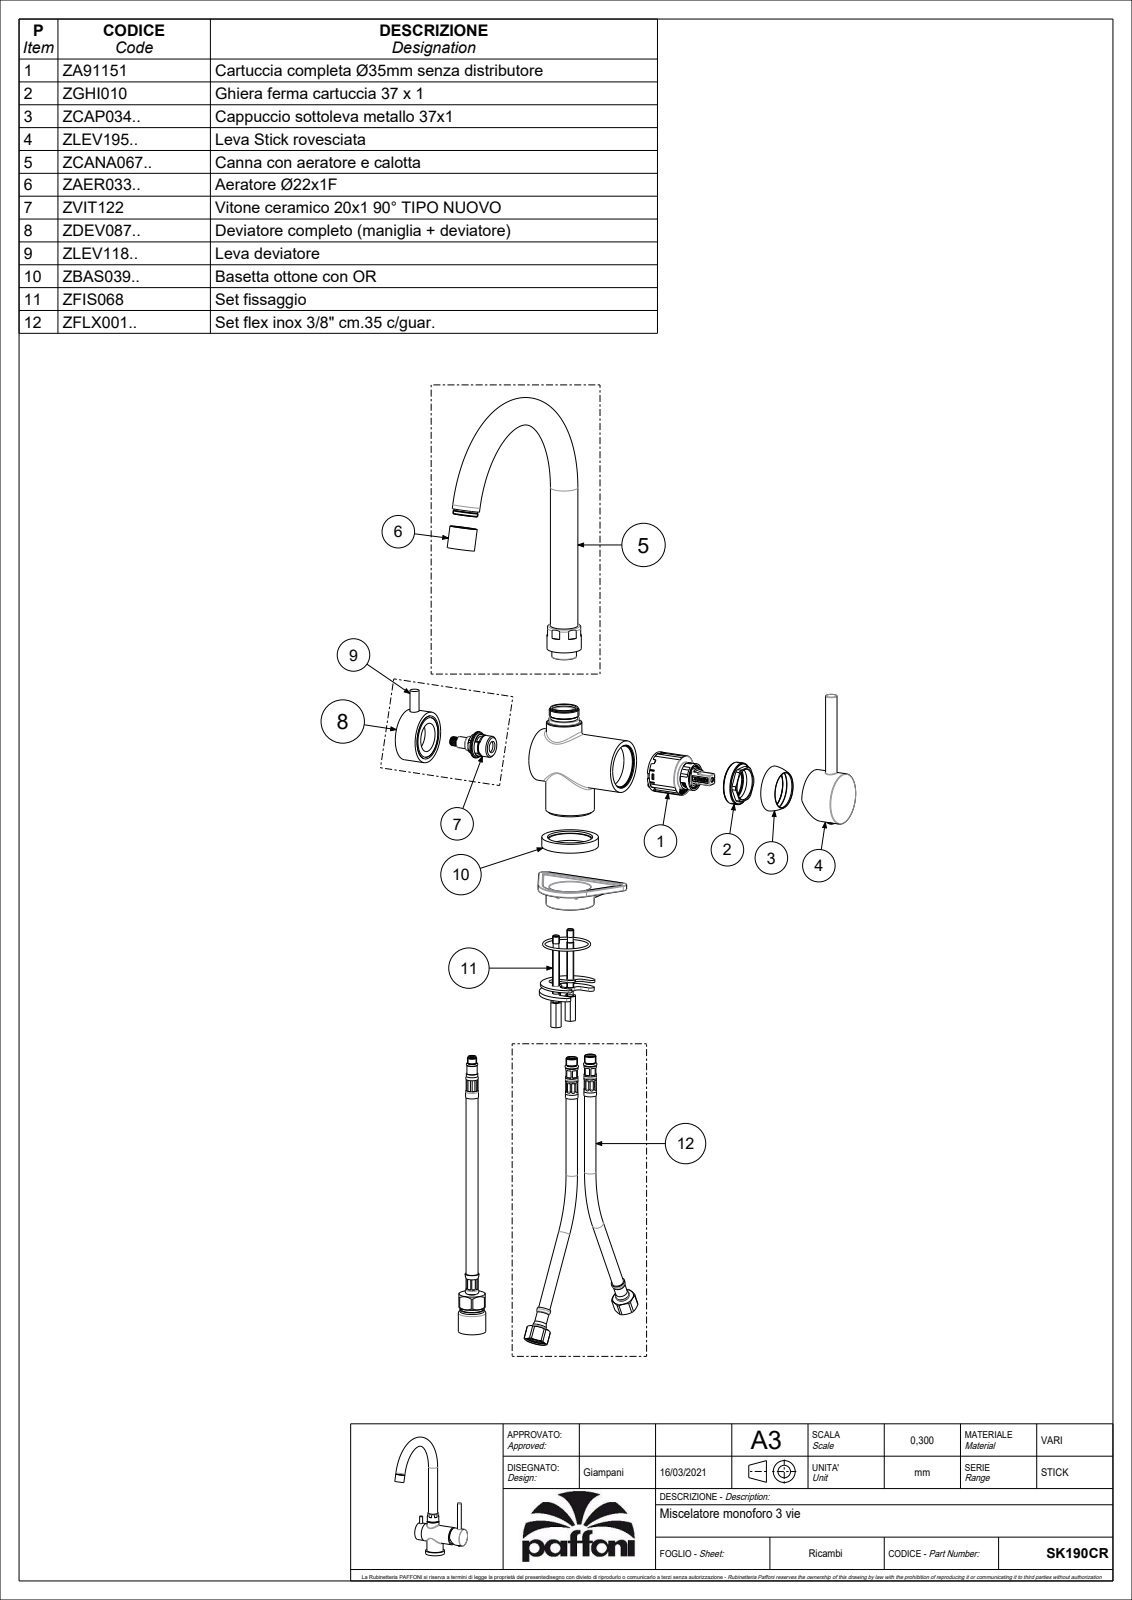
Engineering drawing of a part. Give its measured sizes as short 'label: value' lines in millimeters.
name: SK190CR
written by: CREO PARAMETRIC BY PTC INC, 2020044 (CONFIG_CONTROL_DESIGN)
unit: mm
bodies: 4 solids, 476 faces (157 planar, 153 cylindrical, 166 other)
size: 333.3 × 213.15 × 135.38
volume: 233 313 mm³; area: 123 797 mm²
holes: 8× ⌀7, 4× ⌀5, 2× ⌀5.5, 2× ⌀9, 2× ⌀11, 2× ⌀21, 1× ⌀3, 1× ⌀4.2, 1× ⌀5.6, 1× ⌀8.6, 1× ⌀9.4, 1× ⌀15
bosses: 2× ⌀24, 1× ⌀49.5, 1× ⌀45.6, 1× ⌀44.7, 1× ⌀44.5, 1× ⌀42.5, 1× ⌀38.7, 1× ⌀35
rounds: 8× R0.5, 1× R2.75, 1× R22.29
face distances: 95.47, 51.8, 51.5, 6.5, 6.47, 0.33, 51.47, 1.5, 95.77, 95.44
hole spacings: 9.01, 9.6, 10.42, 12.3, 12.5, 12.66, 12.85, 13.45
